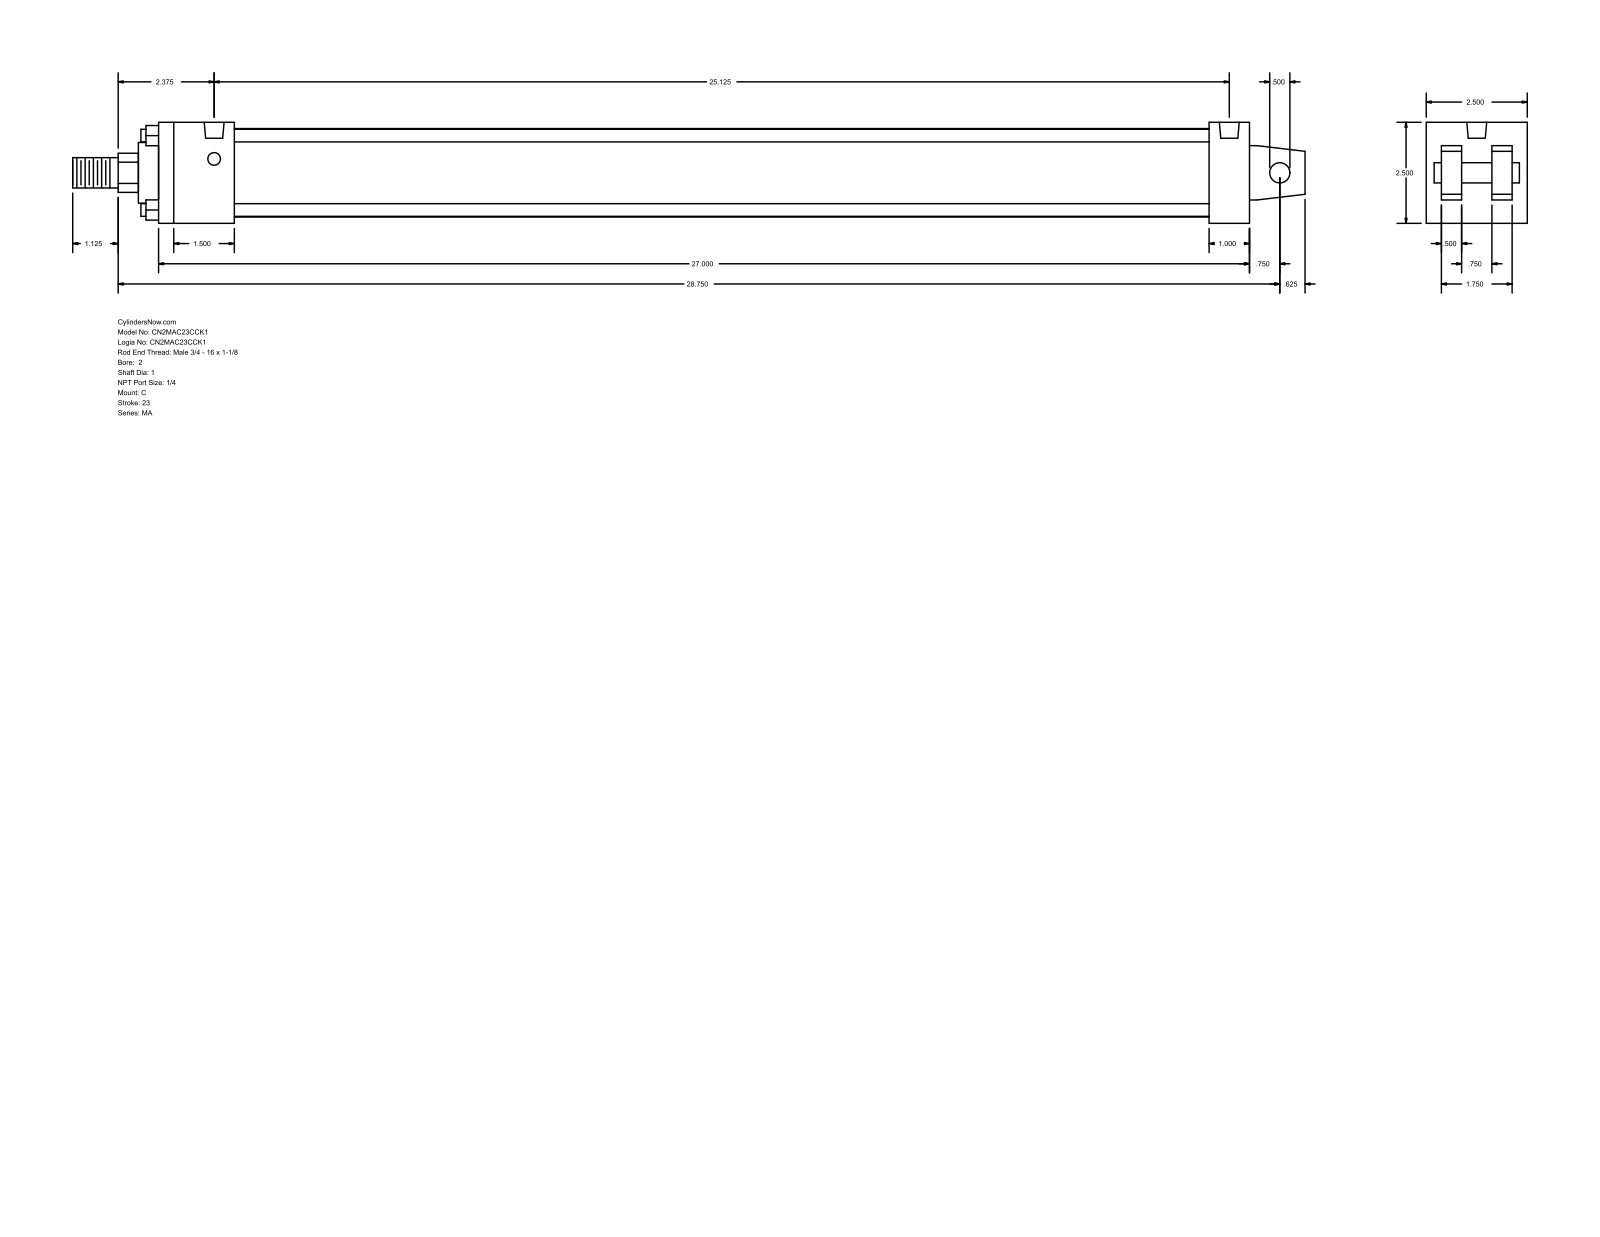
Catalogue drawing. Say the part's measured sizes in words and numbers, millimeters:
The part is named "MA_C__0200_1". Its 3-D file was written by "GSSL Pune (CONFIG_CONTROL_DESIGN)". It is 0 solids with 103 faces: 76 planar, 27 cylindrical and 0 other. Overall it measures 774.7 by 63.5 by 63.5 millimeters. Round holes: 4 of diameter 7.94, 2 of diameter 12.49. Round bosses or shafts: 4 of diameter 7.94, 1 of diameter 55.63, 1 of diameter 38.1, 1 of diameter 25.4, 1 of diameter 19.05, 1 of diameter 12.7. Partial cylindrical surfaces (rounded edges, fillets, slot ends): 1 of radius 12.29. The main face-to-face distances are 63.5, 12.7, 685.8, 22.22, 41.28, 9.52, 53.98, 31.76, 47.63, 25.4. The hole center spacings are 638.17.
